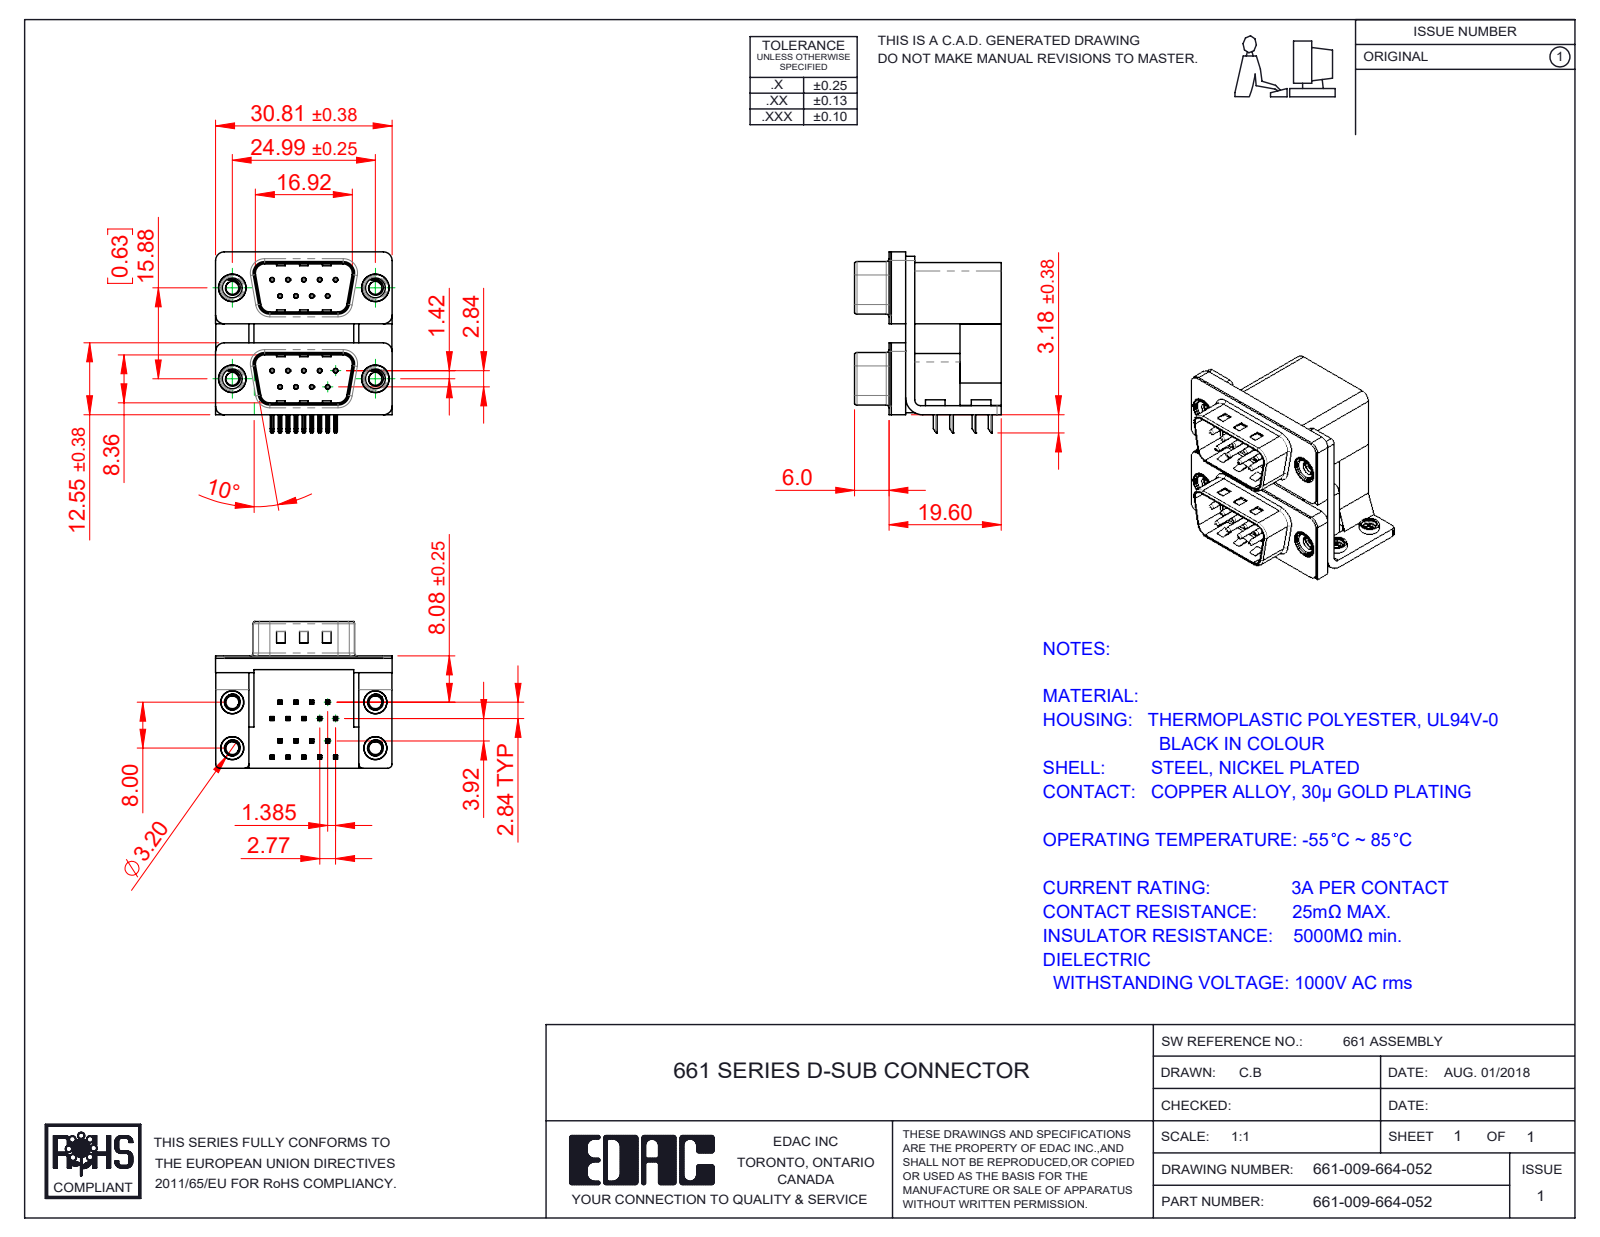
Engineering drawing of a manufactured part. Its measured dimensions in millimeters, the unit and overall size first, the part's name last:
Units: millimetres
Overall size (bounding box): 31.61 × 30.81 × 25.6
Round holes (diameter × count): ⌀0.35 ×18, ⌀0.8 ×18, ⌀2.26 ×8, ⌀2.75 ×4, ⌀3.2 ×4, ⌀3.5 ×4, ⌀4 ×4, ⌀4.8 ×4, ⌀5 ×4
Round bosses / shafts (diameter × count): ⌀0.75 ×18, ⌀4.9 ×4, ⌀4.75 ×4, ⌀4 ×4, ⌀3.9 ×4, ⌀3.4 ×4
Partial cylindrical surfaces — rounded edges, fillets, slot ends (radius × count): R0.25 ×72, R0.12 ×36, R0.5 ×16, R1.5 ×13, R0.75 ×8, R0.9 ×8, R1.6 ×8, R2 ×8
Main face-to-face distances: 0.4, 2.5, 16.7, 19.2, 15.87, 1.6, 7.2, 9.5, 12, 19.6
Hole centre spacings: 3.16, 16.12, 2.77, 15.88, 16.82, 18.77, 5.54, 5.04
Volume: 9 873 mm³ · Surface area: 11 657 mm²
Bodies: 33 solids, 2088 faces (1164 planar, 670 cylindrical, 254 other)
Part name (STEP PRODUCT): 661 4-40 Threaded Board Mount; 661 Housing Upper_09 Contacts L; 661 Contact Bottom Lower; 661 Contact Top Lower (+8 more)
STEP written by: SolidWorks 2020 (CONFIG_CONTROL_DESIGN)
